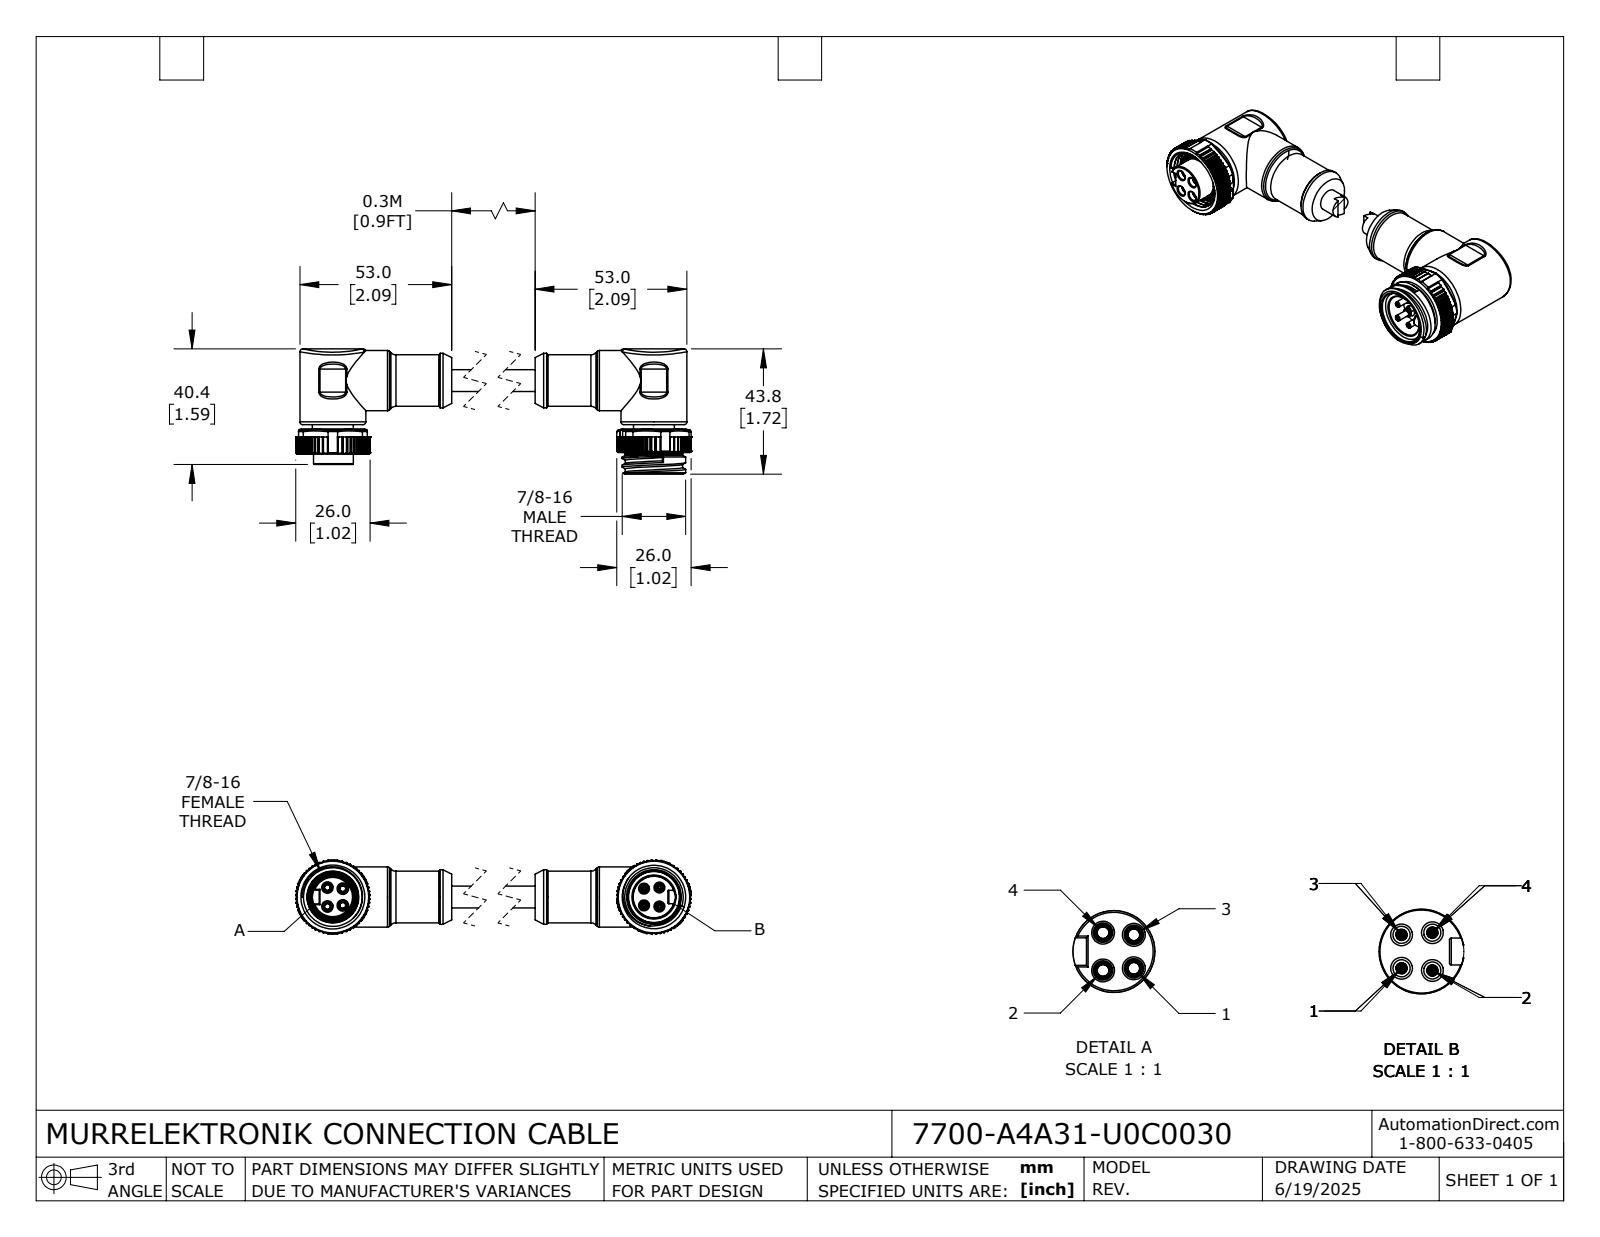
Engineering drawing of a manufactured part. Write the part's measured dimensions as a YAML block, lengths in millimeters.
part_name: "7700-A4A31-U0C0030_MALE; 7700-A4A31-U0C0030_FEMALE; 7700-A4A31-U0C0030"
step_written_by: "SolidWorks 2024 (CONFIG_CONTROL_DESIGN)"
units: millimeters
bodies: {solids: 2, faces: 1268, planar: 520, cylindrical: 581, other: 167}
overall_size: [138.97, 43.76, 26]
volume: 49781
surface_area: 17240
round_holes:
  - {diameter: 2.05, count: 4}
  - {diameter: 3, count: 4}
  - {diameter: 3.4, count: 4}
  - {diameter: 15.6, count: 2}
  - {diameter: 15.5, count: 1}
  - {diameter: 18.5, count: 1}
  - {diameter: 20.5, count: 1}
  - {diameter: 22.22, count: 1}
round_bosses_or_shafts:
  - {diameter: 3, count: 4}
  - {diameter: 2, count: 4}
  - {diameter: 23, count: 2}
  - {diameter: 18.1, count: 2}
  - {diameter: 17.8, count: 2}
  - {diameter: 14.3, count: 2}
  - {diameter: 22.17, count: 1}
  - {diameter: 21, count: 1}
partial_cylinders:
  - {radius: 0.2, count: 252}
  - {radius: 0.3, count: 34}
  - {radius: 0.1, count: 8}
  - {radius: 1, count: 8}
  - {radius: 0.7, count: 4}
  - {radius: 0.73, count: 4}
  - {radius: 2.5, count: 4}
  - {radius: 13, count: 2}
face_to_face_distances: [1.5, 8.8, 7.3, 9.7, 0.9, 7, 30, 8.2, 21, 4.2]
hole_center_spacings: [3.81, 4.54, 5.39, 8.22, 109.56, 114.95, 5.84, 6.6]
